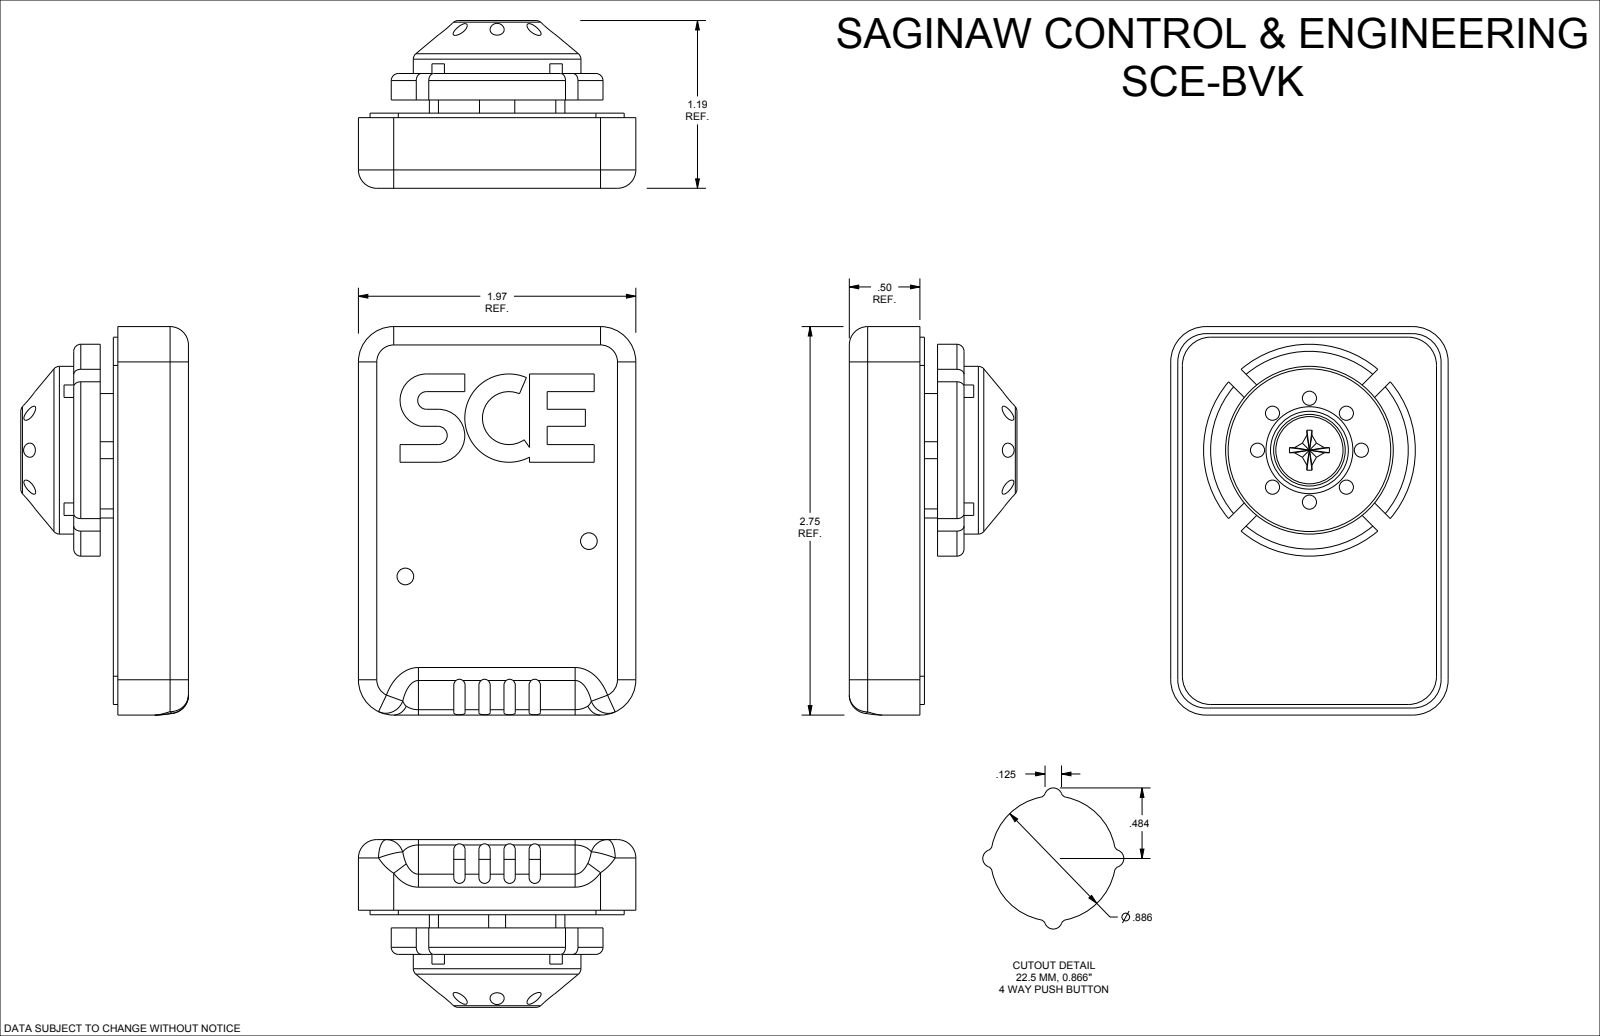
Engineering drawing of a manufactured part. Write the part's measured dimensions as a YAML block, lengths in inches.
part_name: "SCE-BVK"
step_written_by: "SolidWorks 2019 (AUTOMOTIVE_DESIGN)"
units: inches
bodies: {solids: 6, faces: 239, planar: 108, cylindrical: 86, other: 45}
overall_size: [2.75, 1.965, 1.188]
volume: 2.575
surface_area: 40.83
round_holes:
  - {diameter: 0.1, count: 8}
  - {diameter: 0.118, count: 2}
  - {diameter: 0.25, count: 1}
  - {diameter: 0.281, count: 1}
  - {diameter: 0.344, count: 1}
  - {diameter: 0.845, count: 1}
  - {diameter: 1.026, count: 1}
round_bosses_or_shafts:
  - {diameter: 1.5, count: 1}
  - {diameter: 1.187, count: 1}
  - {diameter: 1.085, count: 1}
  - {diameter: 0.84, count: 1}
  - {diameter: 0.44, count: 1}
  - {diameter: 0.343, count: 1}
  - {diameter: 0.248, count: 1}
partial_cylinders:
  - {radius: 0.04, count: 16}
  - {radius: 0.13, count: 11}
  - {radius: 0.2, count: 8}
  - {radius: 0.06, count: 5}
  - {radius: 0.03, count: 4}
  - {radius: 0.25, count: 4}
  - {radius: 0.062, count: 2}
  - {radius: 0.063, count: 2}
face_to_face_distances: [0.062, 0.532, 0.47, 0.392, 0.33, 0.14, 0.26, 1.705, 0.125, 0.312]
hole_center_spacings: [0.282, 0.682, 0.368, 0.37, 0.52, 0.524, 0.735, 0.741]
